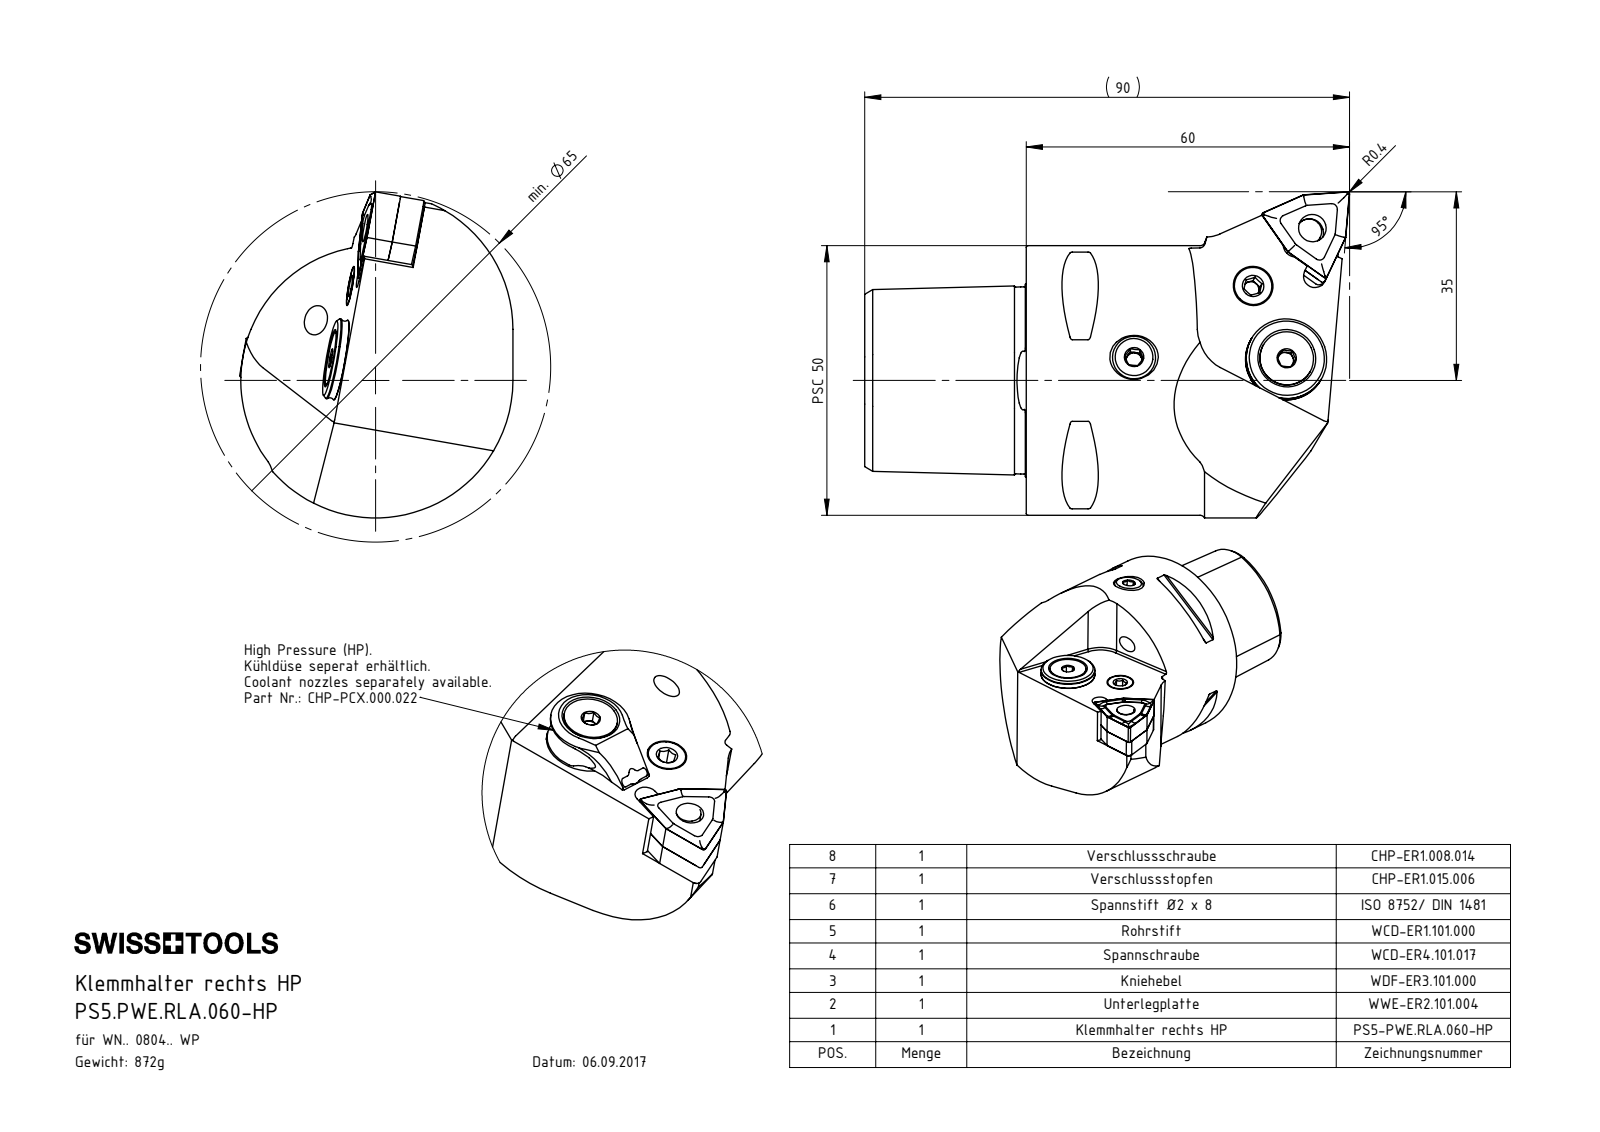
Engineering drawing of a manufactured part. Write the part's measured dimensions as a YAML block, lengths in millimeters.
part_name: "PS5.PWE.RLA.060-HP; CHP-ER1.015.006_A; WCD-ER4.101.017_A; WNMG080404 (+8 more)"
step_written_by: "SolidWorks 2017 (AUTOMOTIVE_DESIGN)"
units: millimeters
bodies: {solids: 11, faces: 467, planar: 141, cylindrical: 116, other: 210}
overall_size: [90, 60.5, 50.73]
volume: 110469
surface_area: 25663
round_holes:
  - {diameter: 4.2, count: 3}
  - {diameter: 7, count: 2}
  - {diameter: 1.2, count: 1}
  - {diameter: 2, count: 1}
  - {diameter: 2.5, count: 1}
  - {diameter: 3, count: 1}
  - {diameter: 4, count: 1}
  - {diameter: 5, count: 1}
  - {diameter: 5.16, count: 1}
  - {diameter: 5.2, count: 1}
  - {diameter: 6.1, count: 1}
  - {diameter: 6.7, count: 1}
round_bosses_or_shafts:
  - {diameter: 8, count: 2}
  - {diameter: 50, count: 1}
  - {diameter: 15, count: 1}
  - {diameter: 13.4, count: 1}
  - {diameter: 10, count: 1}
  - {diameter: 7.9, count: 1}
  - {diameter: 6.4, count: 1}
  - {diameter: 5.5, count: 1}
partial_cylinders:
  - {radius: 0.5, count: 10}
  - {radius: 0.4, count: 3}
  - {radius: 1, count: 3}
  - {radius: 2.5, count: 3}
  - {radius: 3.2, count: 2}
  - {radius: 7, count: 2}
  - {radius: 25.5, count: 2}
  - {radius: 2.1, count: 1}
face_to_face_distances: [30, 4.76, 4.46, 4.5, 9.22, 4.72, 19.18, 44.4, 5, 10]
hole_center_spacings: [15.6, 21.59, 25.38, 4.49, 4.5, 4.51, 4.52, 10.64]
